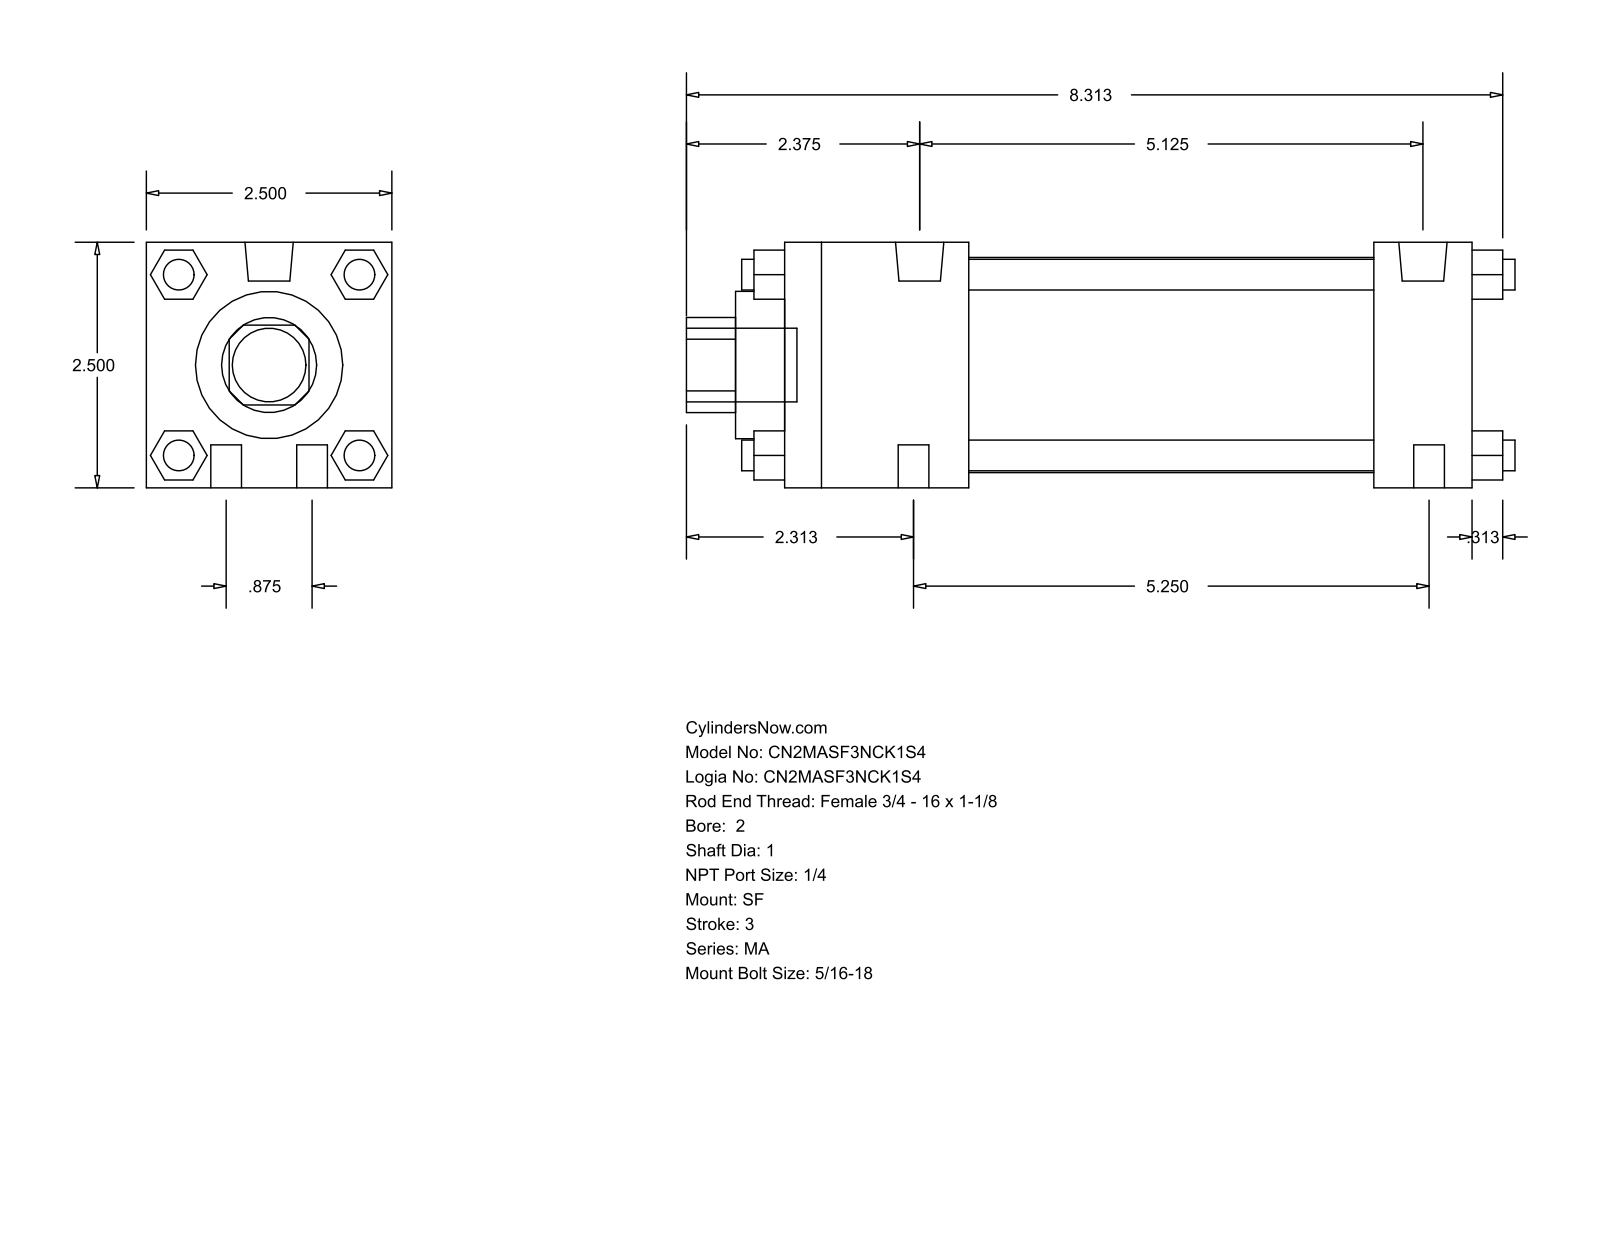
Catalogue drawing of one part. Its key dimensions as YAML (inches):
part_name: "MA_SF__0200_1"
step_written_by: "GSSL Pune (CONFIG_CONTROL_DESIGN)"
units: inches
bodies: {solids: 0, faces: 124, planar: 94, cylindrical: 30, other: 0}
overall_size: [8.437, 2.5, 2.5]
round_holes:
  - {diameter: 1, count: 1}
  - {diameter: 1.5, count: 1}
  - {diameter: 2.19, count: 1}
round_bosses_or_shafts:
  - {diameter: 0.313, count: 10}
  - {diameter: 0.492, count: 2}
  - {diameter: 0.75, count: 1}
partial_cylinders:
  - {radius: 0.484, count: 1}
face_to_face_distances: [2.5, 7, 0.5, 1, 6, 1.875, 4.125, 5.125, 0.92, 1.593]
